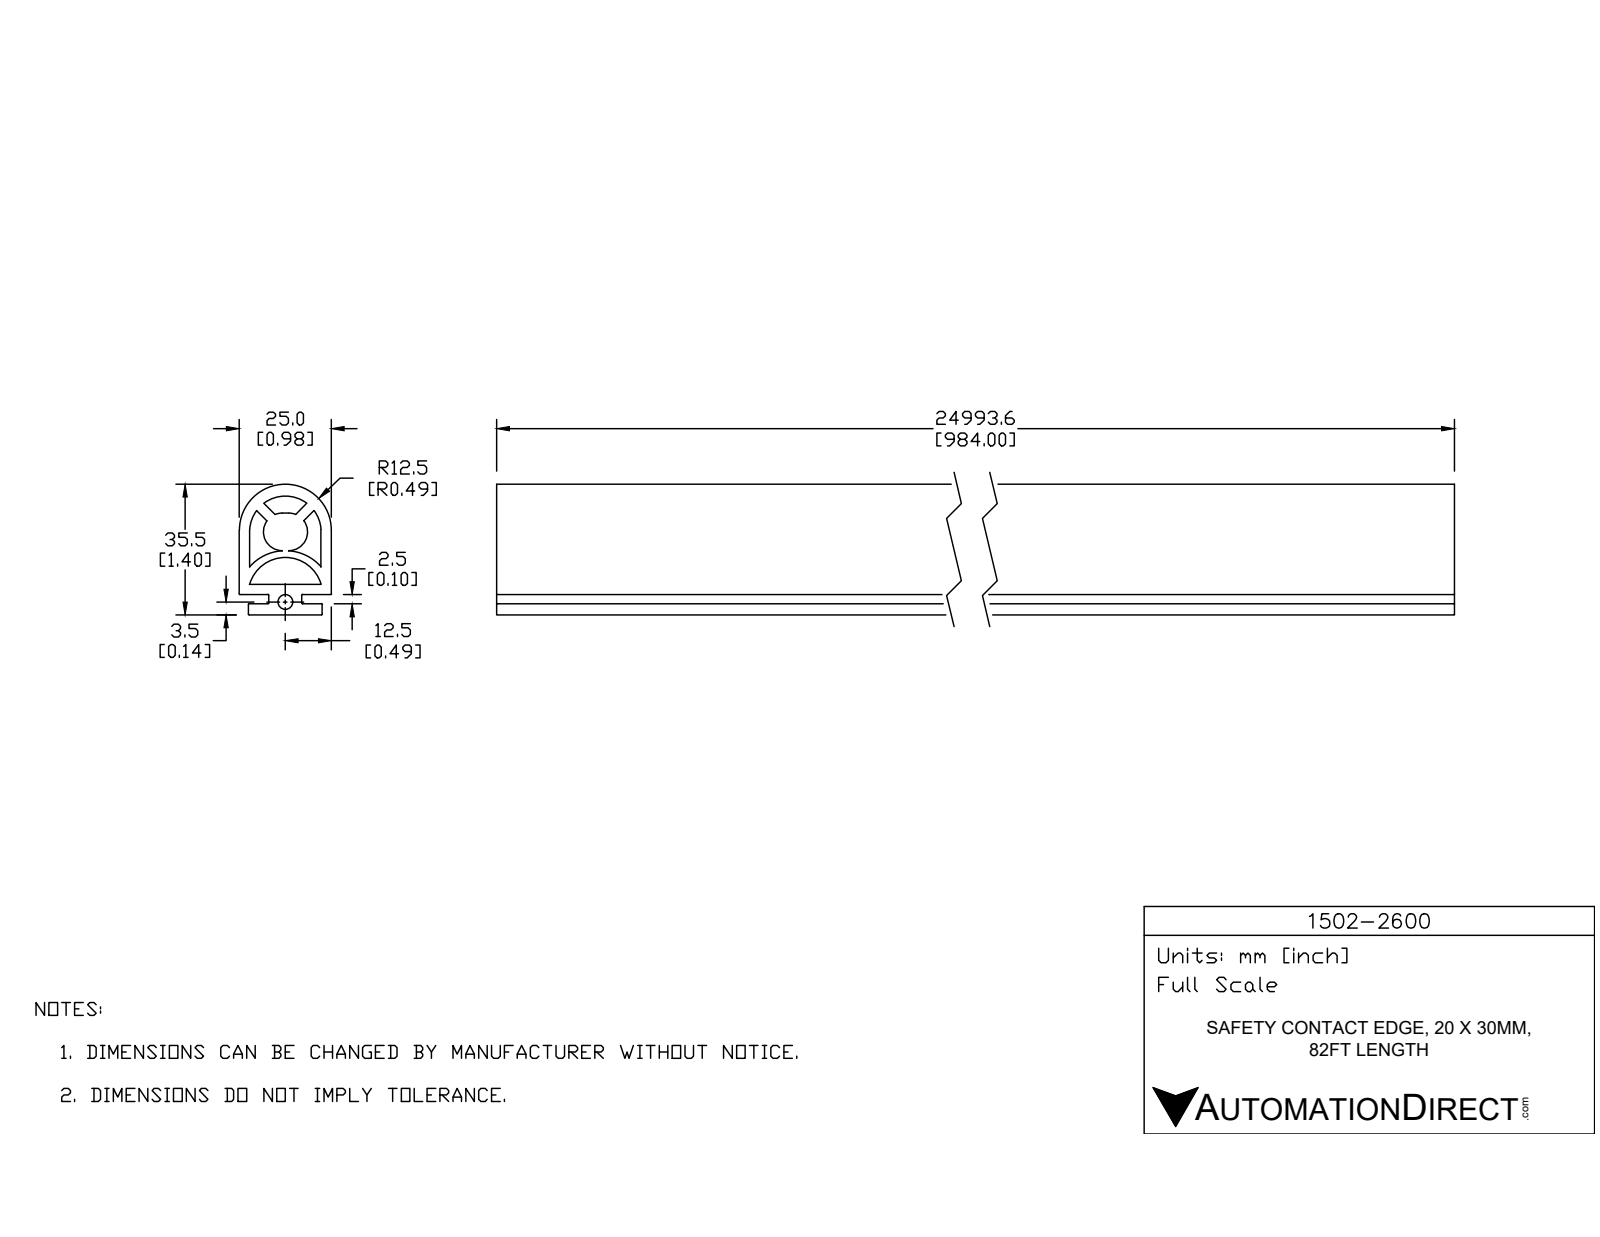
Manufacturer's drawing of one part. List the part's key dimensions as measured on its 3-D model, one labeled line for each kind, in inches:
Part name (STEP PRODUCT): 1502-2600
STEP written by: SolidWorks 2017 (AUTOMOTIVE_DESIGN)
Units: inches
Bodies: 1 solid, 47 faces (23 planar, 24 cylindrical, 0 other)
Overall size (bounding box): 24 × 1.398 × 0.984
Volume: 18.57 in³ · Surface area: 283.1 in²
Round holes (diameter × count): ⌀0.157 ×1
Partial cylindrical surfaces — rounded edges, fillets, slot ends (radius × count): R0.008 ×10, R0.202 ×2, R0.382 ×1, R0.398 ×1, R0.492 ×1, R0.508 ×1
Main face-to-face distances: 0.11, 0.217, 0.327, 0.984, 0.098, 0.118, 0.209, 0.112, 0.872, 0.874
